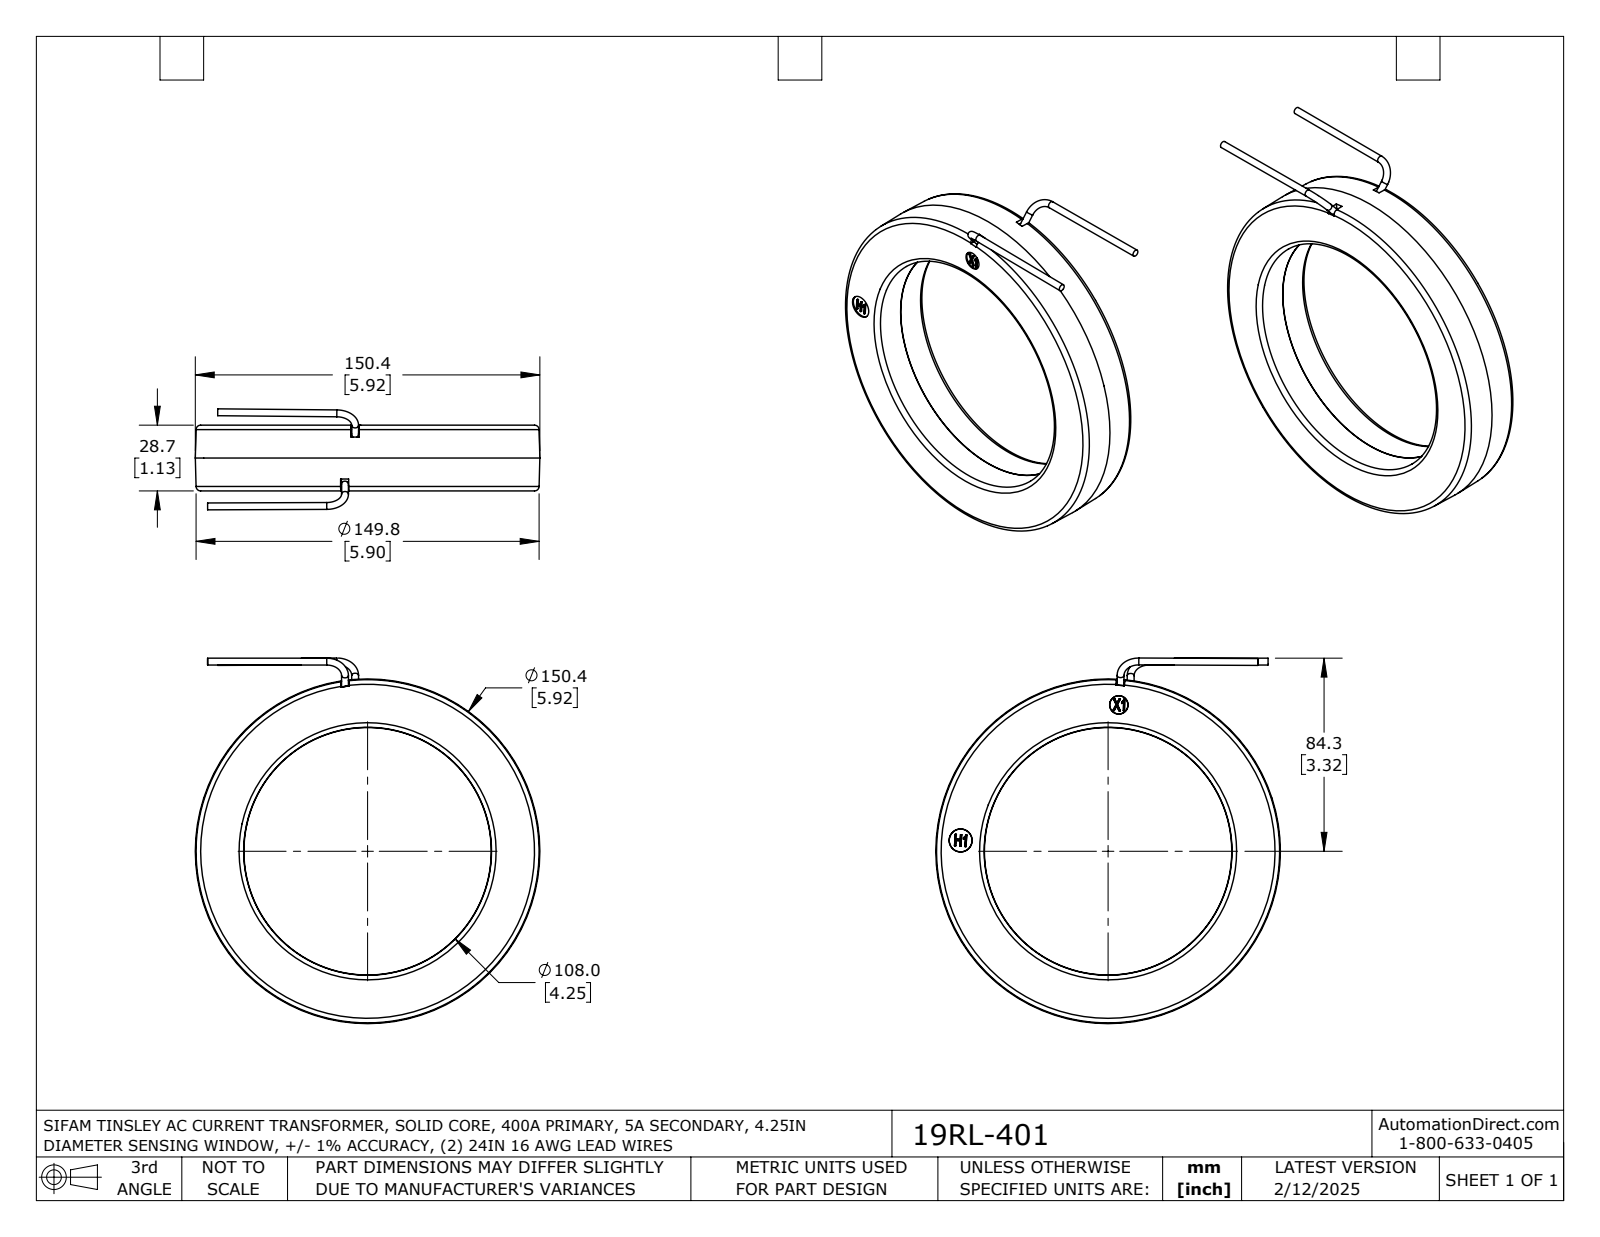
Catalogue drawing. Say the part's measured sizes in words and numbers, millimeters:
The part is named "19RL-401". Its 3-D file was written by "SolidWorks 2021 (AUTOMOTIVE_DESIGN)". It is 1 solid with 104 faces: 52 planar, 8 cylindrical and 44 other. Overall it measures 159.6 by 150.4 by 44 millimeters. Its volume is 242 700 cubic millimeters and its surface area 55 080 square millimeters. Round bosses or shafts: 4 of diameter 3. The main face-to-face distances are 14.3, 14.4, 28.7, 28.2, 13.9, 13.8, 0.5, 28.2, 13.9, 13.8.
